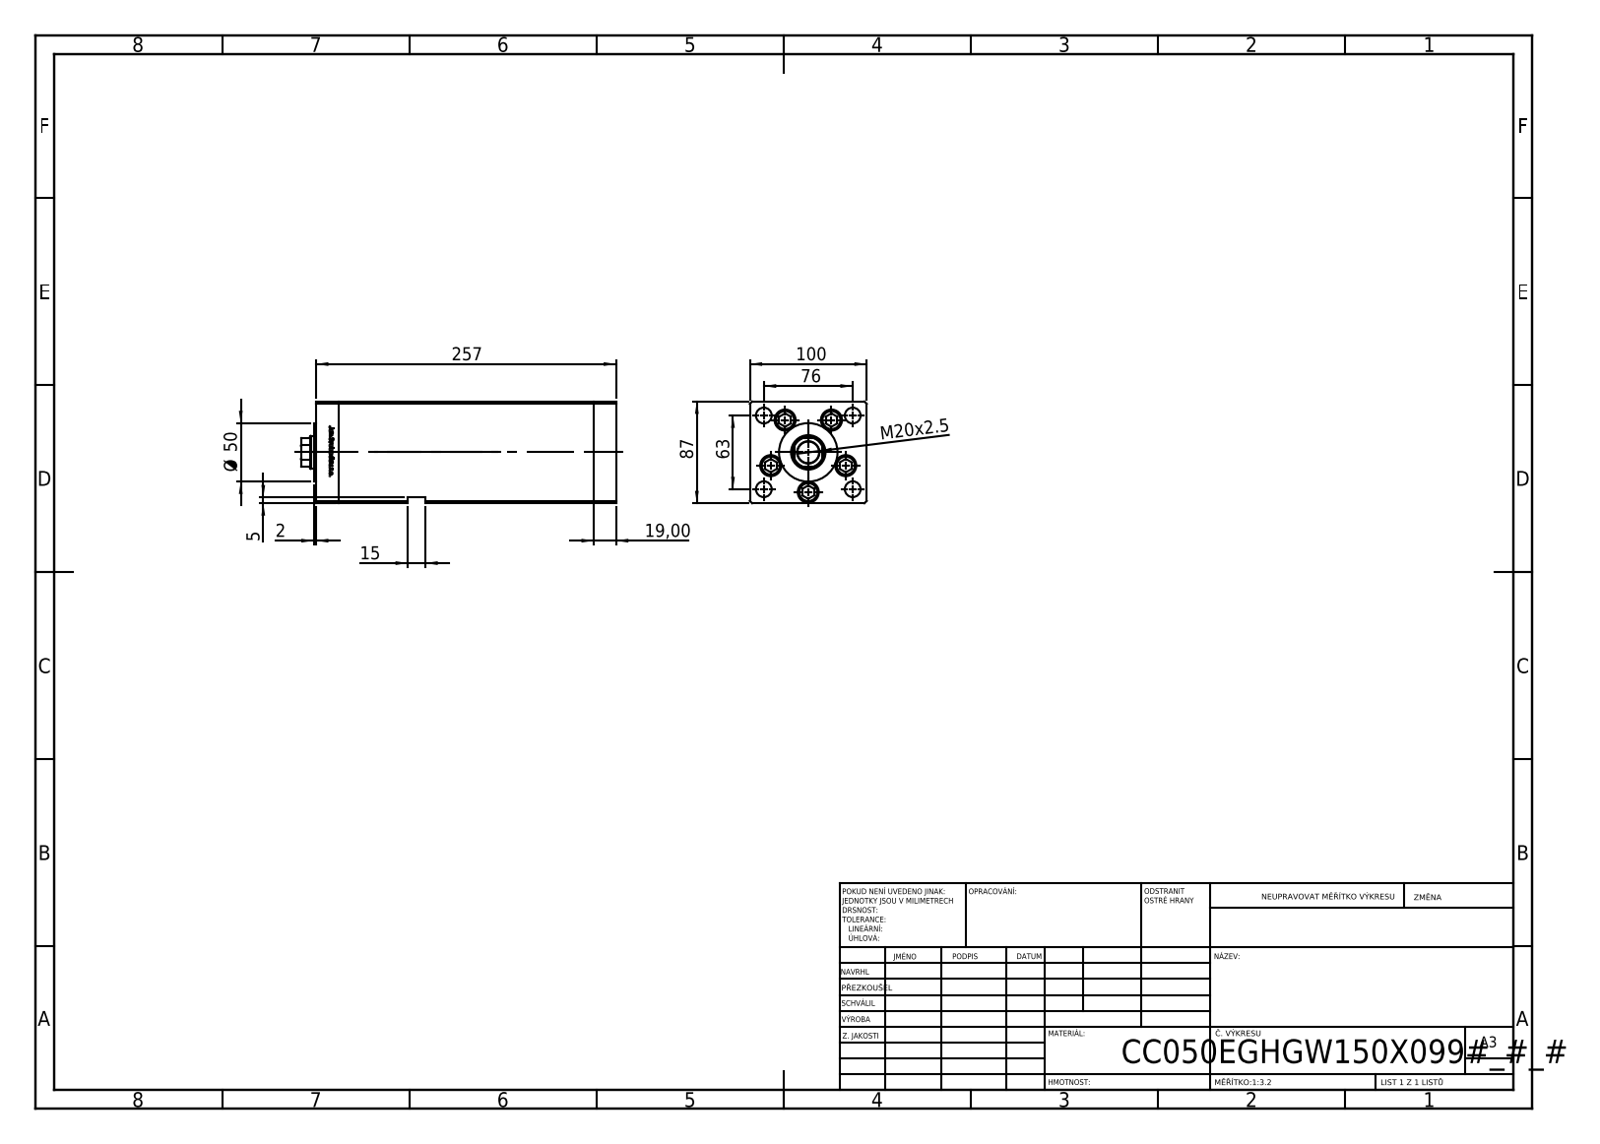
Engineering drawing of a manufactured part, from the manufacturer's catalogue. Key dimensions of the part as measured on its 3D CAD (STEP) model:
Part name (STEP PRODUCT): V220C BACK_E; V220C_FRONT_E; V220C_E MIDDLE; V220C_VC_E (+1 more)
STEP written by: SolidWorks 2019 (CONFIG_CONTROL_DESIGN)
Units: millimetres
Bodies: 14 solids, 1212 faces (473 planar, 165 cylindrical, 574 other)
Overall size (bounding box): 269.5 × 100 × 87
Volume: 1 865 000 mm³ · Surface area: 265 735 mm²
Round holes (diameter × count): ⌀13.5 ×11, ⌀18 ×5, ⌀18.5 ×5, ⌀12.5 ×4, ⌀2 ×2, ⌀13.16 ×2, ⌀28 ×1, ⌀29.5 ×1
Round bosses / shafts (diameter × count): ⌀17 ×5, ⌀8 ×5, ⌀50 ×1
Partial cylindrical surfaces — rounded edges, fillets, slot ends (radius × count): R0.93 ×2, R13.5 ×1
Main face-to-face distances: 100, 87, 19, 218.5, 237.5, 34.25, 256.5, 15.25, 203.25, 222.25
Hole centre spacings: 34, 18.59, 39.64, 49.36, 57.95, 21.03, 38.08, 39.27
